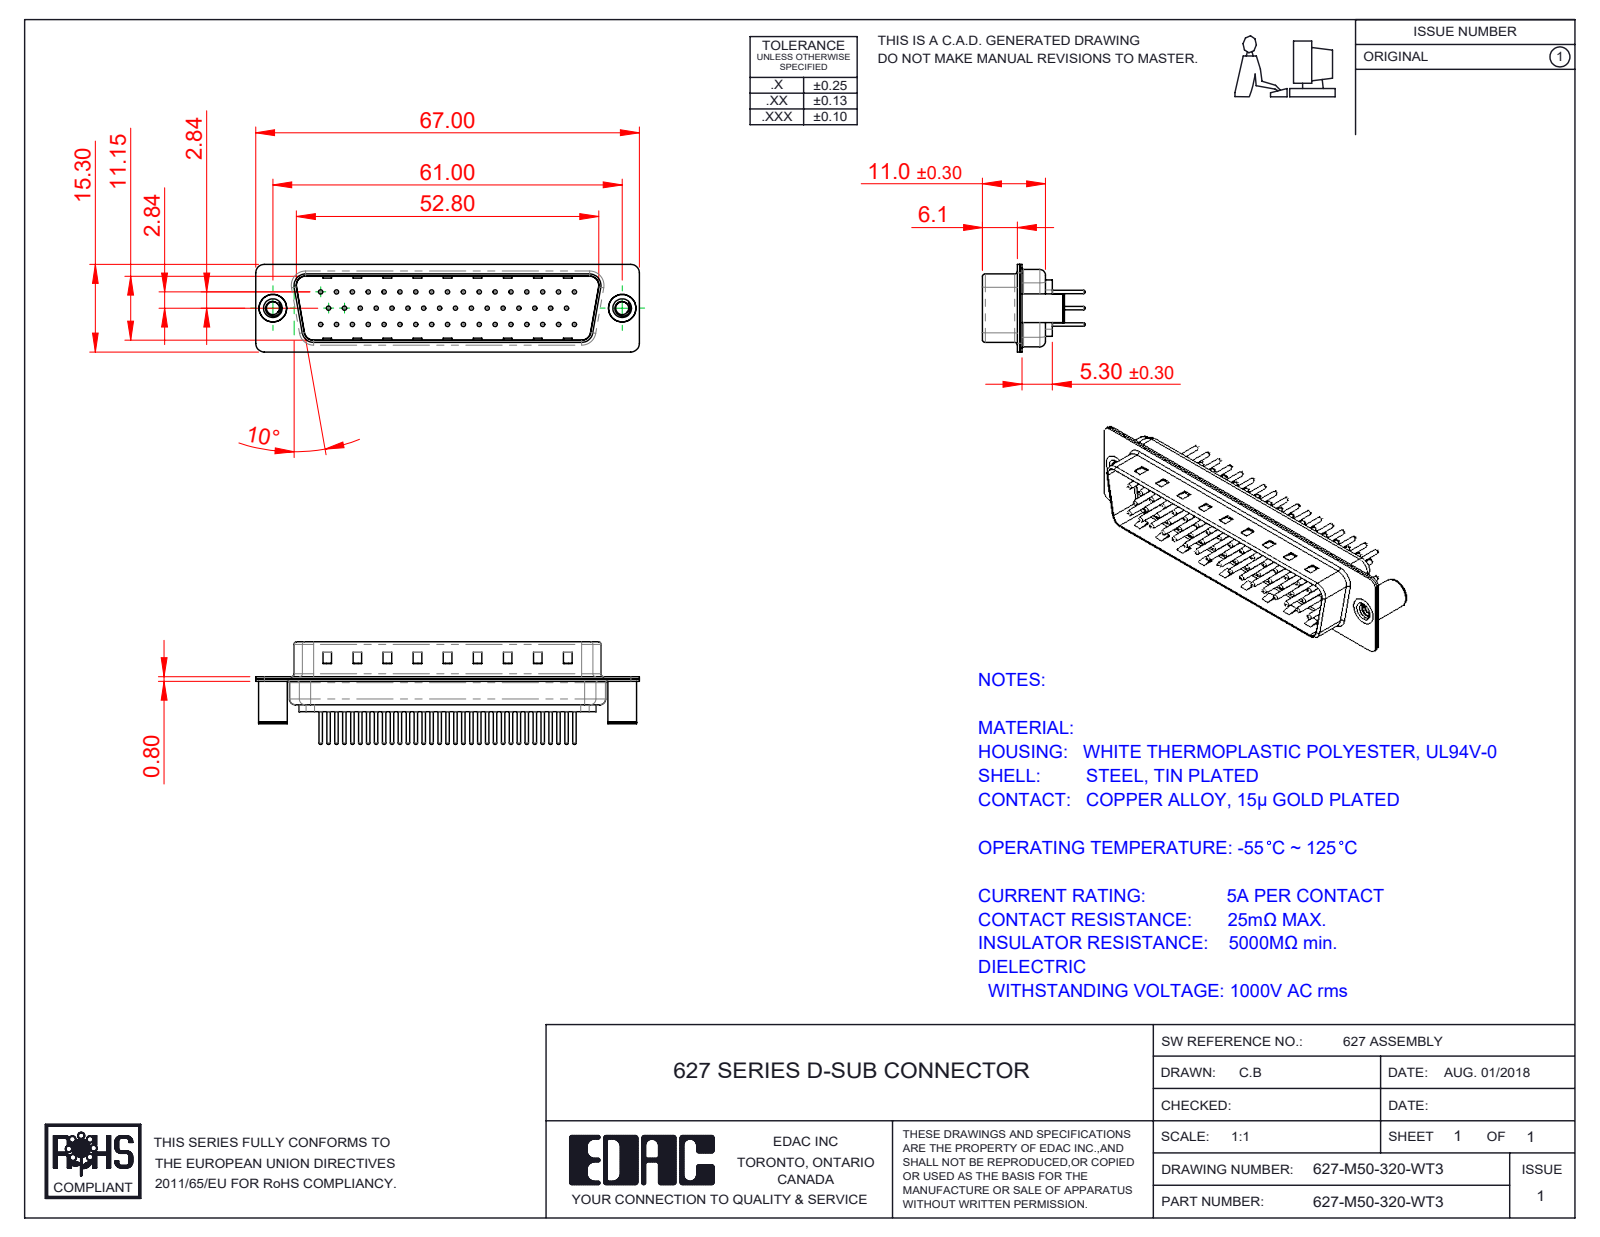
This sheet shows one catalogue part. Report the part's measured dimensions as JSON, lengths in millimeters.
{"part_name": "627M Contact Row 1_20; 627M 4-40 Threaded Board Spacer; 627M Shell Rear_50 Contacts; 627M Contact Row 2_20 (+4 more)", "step_written_by": "SolidWorks 2020 (CONFIG_CONTROL_DESIGN)", "units": "millimeters", "bodies": {"solids": 55, "faces": 2296, "planar": 553, "cylindrical": 865, "other": 878}, "overall_size": [67, 17.9, 15.3], "volume_mm3": 4648, "surface_area_mm2": 10957, "round_holes": [[0.75, 50], [1.6, 50], [2, 50], [2.26, 2], [3.26, 2], [4, 2], [4.8, 2]], "round_bosses_or_shafts": [[1.5, 50], [0.6, 50], [5, 2], [4.9, 2]], "partial_cylinders_radius": [[1.5, 16], [2, 12], [0.5, 8], [1.6, 8], [0.25, 4], [0.6, 4], [0.65, 4], [0.9, 4]], "face_to_face_distances": [0.4, 11.55, 5.7, 6.1, 0.78, 0.77, 12.33, 5.3, 12.32, 13.1], "hole_center_spacings": [3.16, 2.77, 5.54, 8.31, 11.08, 13.85, 16.62, 5.03]}
